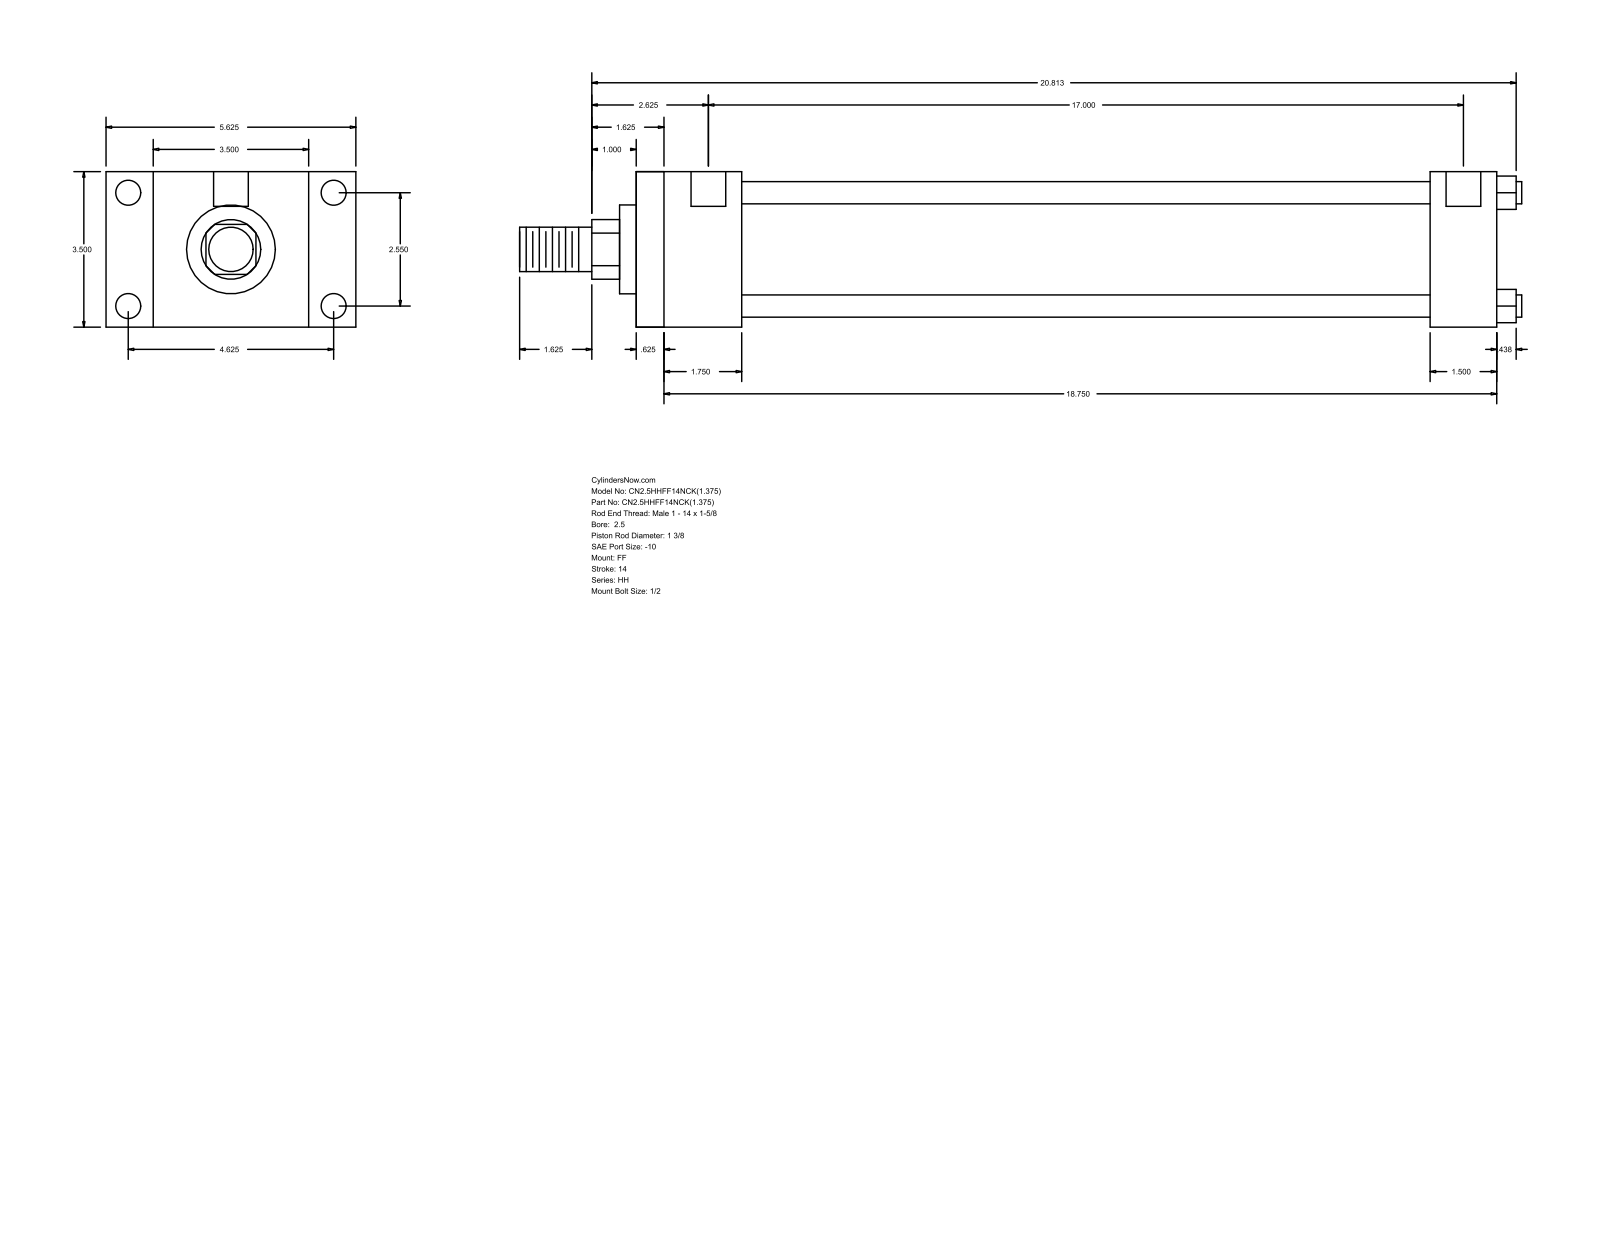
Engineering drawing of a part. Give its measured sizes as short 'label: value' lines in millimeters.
name: HH_FF__0250_1.375
written by: GSSL Pune (CONFIG_CONTROL_DESIGN)
unit: mm
bodies: 0 solids, 92 faces (64 planar, 28 cylindrical, 0 other)
size: 573.09 × 142.88 × 88.9
holes: 4× ⌀5.56, 4× ⌀14.3, 2× ⌀19.84
bosses: 4× ⌀12.7, 1× ⌀73.03, 1× ⌀50.8, 1× ⌀34.92, 1× ⌀25.4
rounds: 1× R17.06
face distances: 88.9, 492.12, 15.87, 476.25, 60.32, 44.45, 431.8, 454.03, 438.16, 393.71
hole spacings: 1.58, 64.76, 117.48, 134.15, 433.39, 434.97, 431.81
